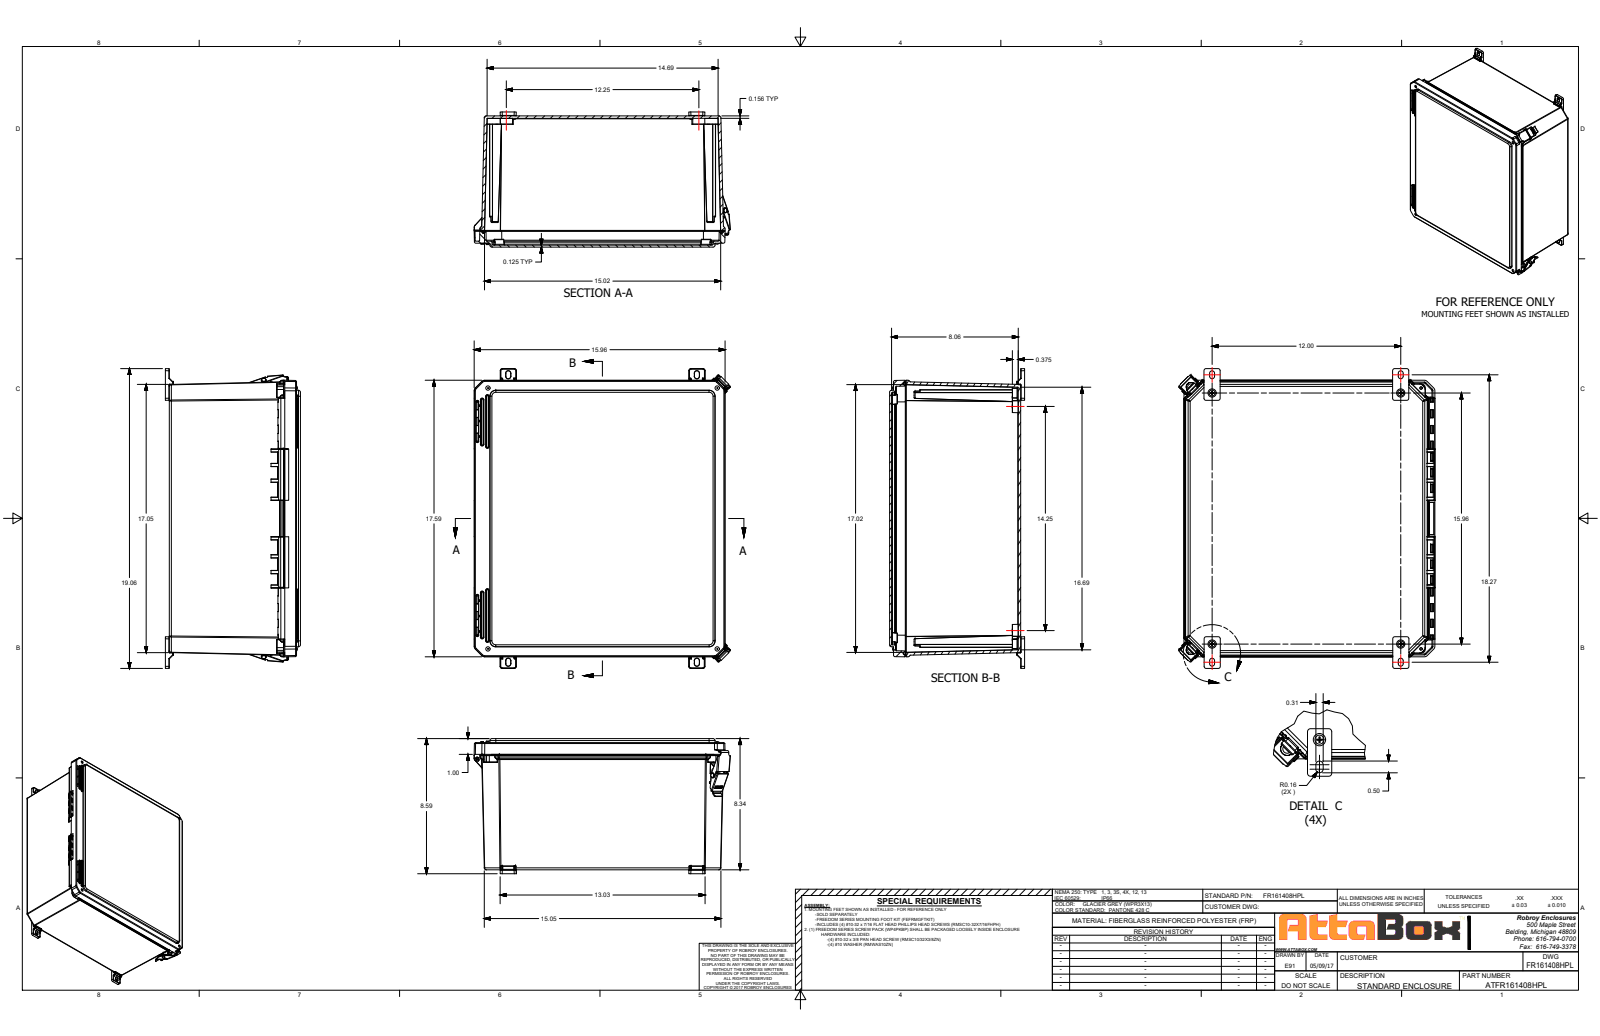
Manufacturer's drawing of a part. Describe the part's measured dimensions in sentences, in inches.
The part is named "FR161408HPL". Its 3-D file was written by "SolidWorks 2021 (AUTOMOTIVE_DESIGN)". It is 29 solids with 2484 faces: 803 planar, 1060 cylindrical and 621 other. Overall it measures 18.253 by 16.292 by 8.84 inches. Its volume is 184.7 cubic inches and its surface area 2 246 square inches. Round holes: 10 of diameter 0.135, 8 of diameter 0.152, 8 of diameter 0.159, 4 of diameter 0.15, 4 of diameter 0.156, 4 of diameter 0.252, 4 of diameter 0.253, 3 of diameter 0.137, 2 of diameter 0.135, 2 of diameter 0.219, 2 of diameter 0.227, 2 of diameter 0.313. Round bosses or shafts: 8 of diameter 0.27, 4 of diameter 0.3, 4 of diameter 0.262, 4 of diameter 0.209, 3 of diameter 0.135, 1 of diameter 0.435, 1 of diameter 0.435. Partial cylindrical surfaces (rounded edges, fillets, slot ends): 189 of radius 0.01, 94 of radius 0.005, 70 of radius 0.02, 70 of radius 0.03, 36 of radius 0.06, 26 of radius 0.09, 24 of radius 0.03, 24 of radius 0.096. The main face-to-face distances are 0.125, 0.156, 8.183, 8.339, 8.058, 8.214, 0.181, 0.179, 0.18, 0.25. The hole center spacings are 15.461, 16.584, 16.585, 20.439, 12.155, 15.106, 19.37, 0.25.
